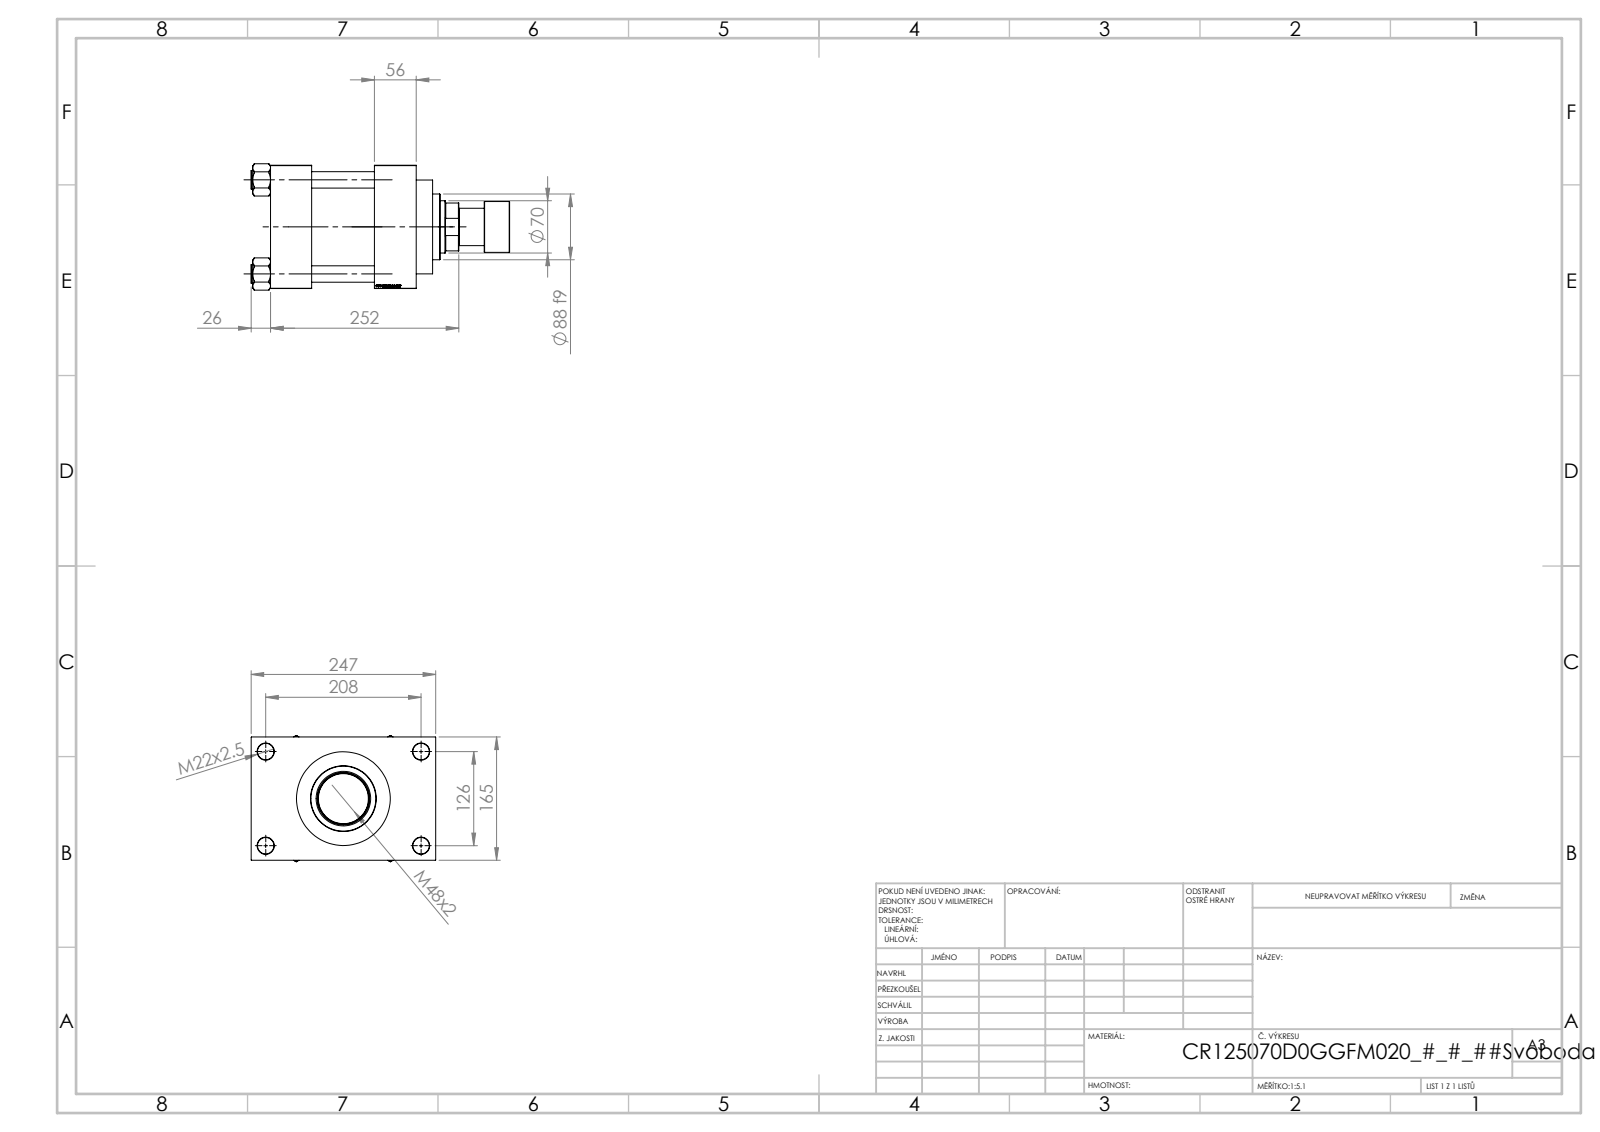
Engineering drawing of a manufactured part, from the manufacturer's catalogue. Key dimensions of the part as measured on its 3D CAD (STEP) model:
Part name (STEP PRODUCT): NUT_M5_D; V215CR_VCP_D; V215CR_D_Body; V215CR_ROD_END_F (+2 more)
STEP written by: SolidWorks 2019 (CONFIG_CONTROL_DESIGN)
Units: millimetres
Bodies: 12 solids, 1163 faces (548 planar, 93 cylindrical, 522 other)
Overall size (bounding box): 346 × 247 × 169.14
Volume: 5 237 000 mm³ · Surface area: 557 775 mm²
Round holes (diameter × count): ⌀22 ×8, ⌀7 ×2, ⌀32.24 ×2, ⌀45 ×2, ⌀46.5 ×1, ⌀70 ×1, ⌀73 ×1, ⌀96 ×1, ⌀125 ×1, ⌀125.5 ×1
Round bosses / shafts (diameter × count): ⌀25 ×4, ⌀131 ×1, ⌀88 ×1, ⌀68 ×1, ⌀50 ×1, ⌀49 ×1
Main face-to-face distances: 165, 84, 55, 139, 195, 140, 56, 41, 206, 173.74
Hole centre spacings: 41.05, 89.02, 121.59, 125.9, 132.47, 166.95, 209.13, 126
